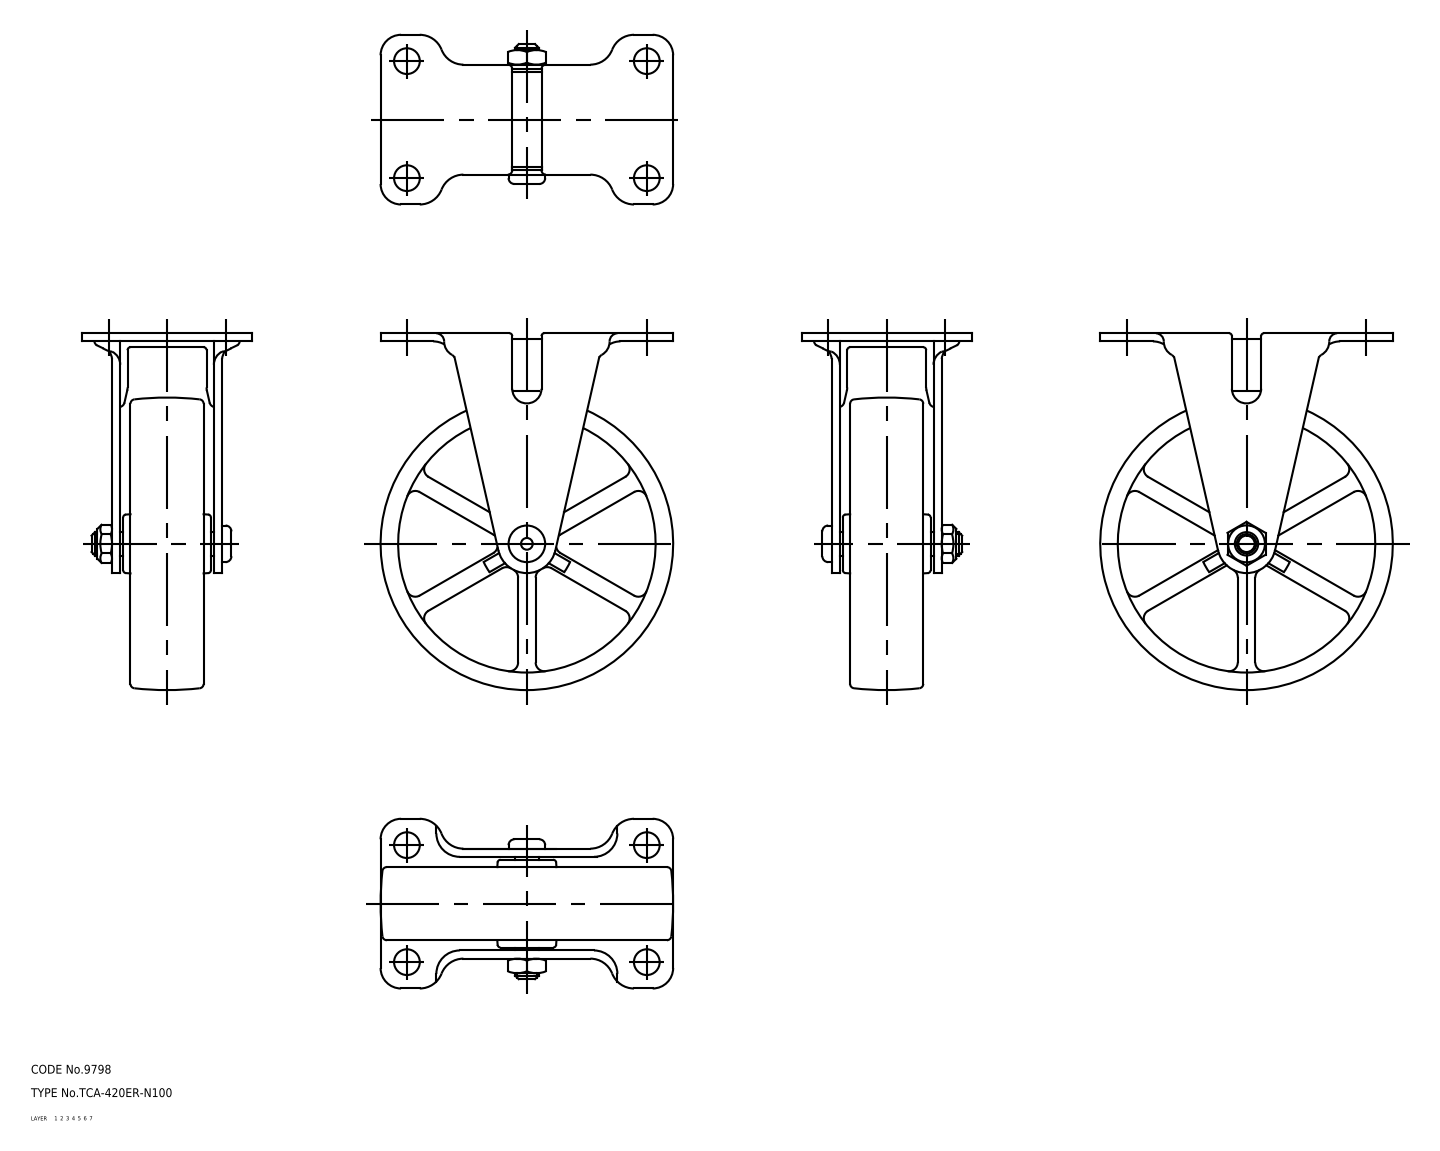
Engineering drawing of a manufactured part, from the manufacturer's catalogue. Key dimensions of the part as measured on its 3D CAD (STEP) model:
Part name (STEP PRODUCT): wheel; axle; No_420_ER_N100_4_29990_36
STEP written by: CADfix (AUTOMOTIVE_DESIGN)
Units: millimetres
Bodies: 3 solids, 566 faces (0 planar, 0 cylindrical, 566 other)
Overall size (bounding box): 122 × 100 × 58
Volume: 172 268 mm³ · Surface area: 50 615 mm²
